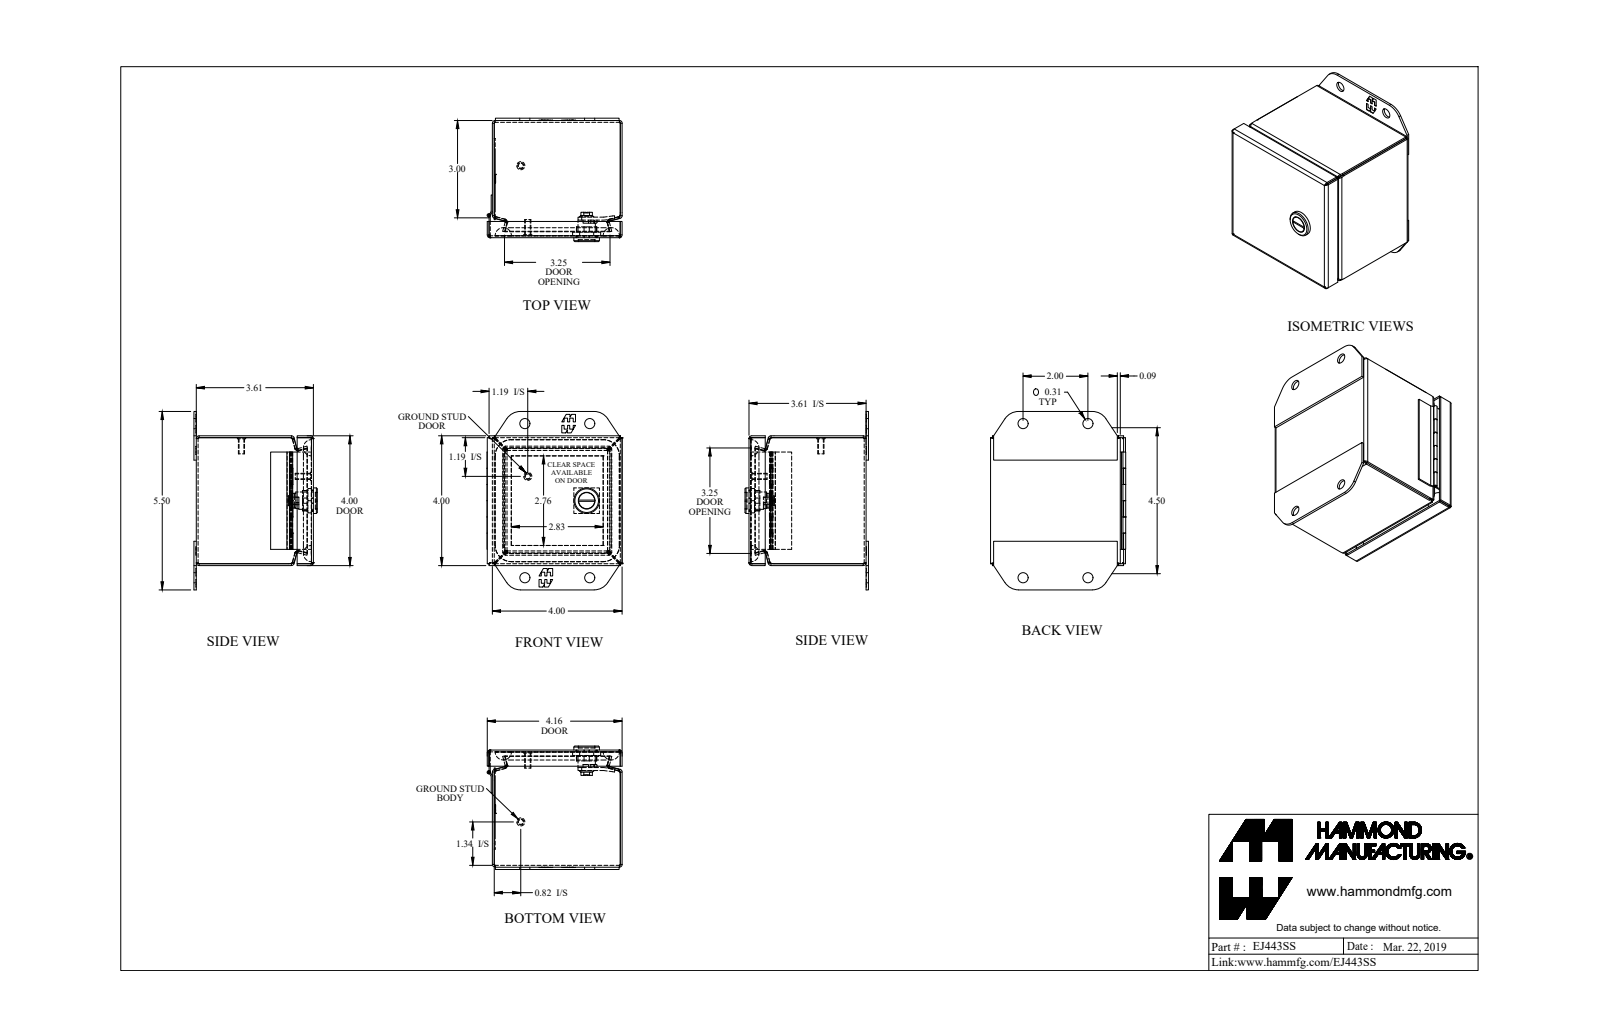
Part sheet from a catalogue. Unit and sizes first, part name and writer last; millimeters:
Units: millimetres
Overall size (bounding box): 139.7 × 105.8 × 96.6
Round holes (diameter × count): ⌀8 ×4, ⌀1.3 ×1, ⌀13.1 ×1
Round bosses / shafts (diameter × count): ⌀6.4 ×2, ⌀4.8 ×2, ⌀20 ×1, ⌀13.6 ×1, ⌀12.6 ×1, ⌀11 ×1, ⌀2.5 ×1, ⌀1.1 ×1
Partial cylindrical surfaces — rounded edges, fillets, slot ends (radius × count): R0.7 ×16, R2.2 ×16, R7.1 ×12, R6.4 ×4, R12.7 ×4, R12.7 ×4, R1.5 ×2, R0.8 ×1
Main face-to-face distances: 1.4, 100.2, 90.3, 98.7, 101.6, 91.7, 88.8, 93.5, 92.1, 3.3
Hole centre spacings: 50.8, 60.4, 77.4, 120.7, 130.9
Volume: 127 500 mm³ · Surface area: 165 900 mm²
Bodies: 11 solids, 530 faces (324 planar, 134 cylindrical, 72 other)
Part name (STEP PRODUCT): EJ443SS_Default
STEP written by: SolidWorks 2019 (CONFIG_CONTROL_DESIGN)
